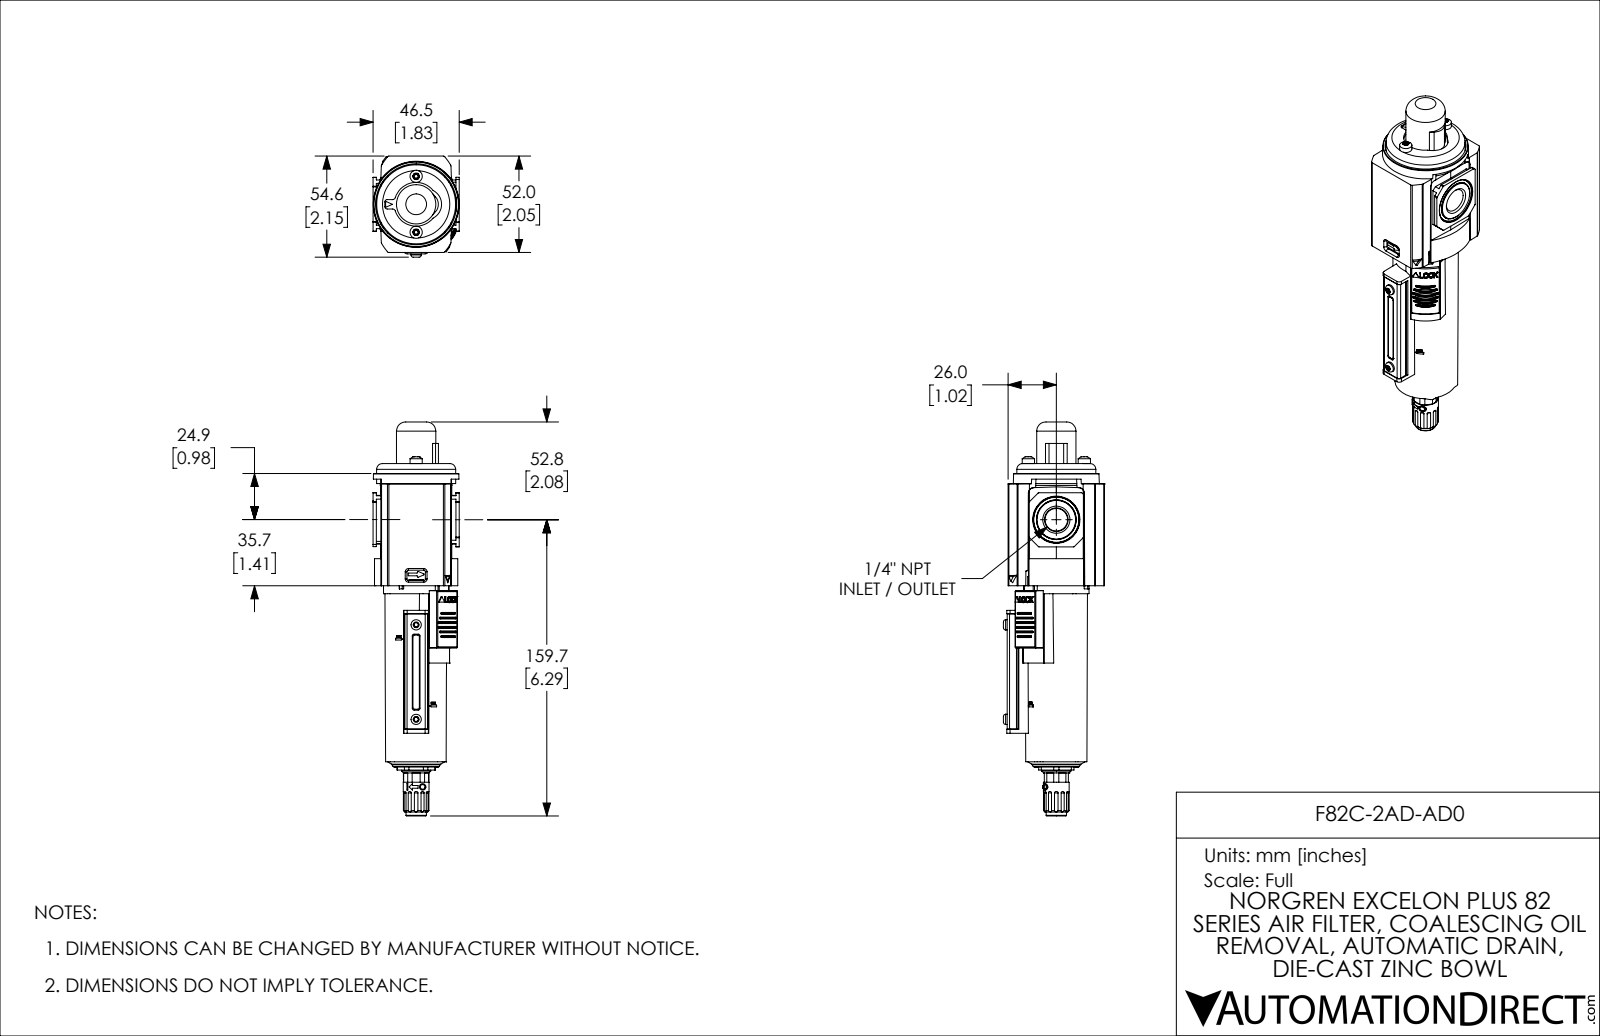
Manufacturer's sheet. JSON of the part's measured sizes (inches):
{"part_name": "F82C-2AD-AD0", "step_written_by": "SolidWorks 2021 (CONFIG_CONTROL_DESIGN)", "units": "inches", "bodies": {"solids": 8, "faces": 1241, "planar": 520, "cylindrical": 506, "other": 215}, "overall_size": [8.367, 2.148, 1.831], "volume_in3": 13.96, "surface_area_in2": 94.2, "round_holes": [[0.059, 2], [0.079, 2], [0.128, 2], [0.173, 2], [0.098, 1], [0.259, 1], [0.628, 1]], "round_bosses_or_shafts": [[0.26, 2], [0.217, 2], [0.157, 2], [1.678, 1], [1.524, 1], [1.388, 1], [1.356, 1], [1.291, 1]], "partial_cylinders_radius": [[0.02, 73], [0.039, 50], [0.011, 12], [0.019, 12], [0.01, 10], [0.031, 8], [0.036, 8], [0.048, 8]], "face_to_face_distances": [0.059, 1.988, 2.047, 1.929, 1.896, 0.182, 1.352, 1.475, 0.123, 1.293], "hole_center_spacings": [0.797, 0.531, 0.594, 0.594, 1.189, 1.063, 1.188, 1.189]}
